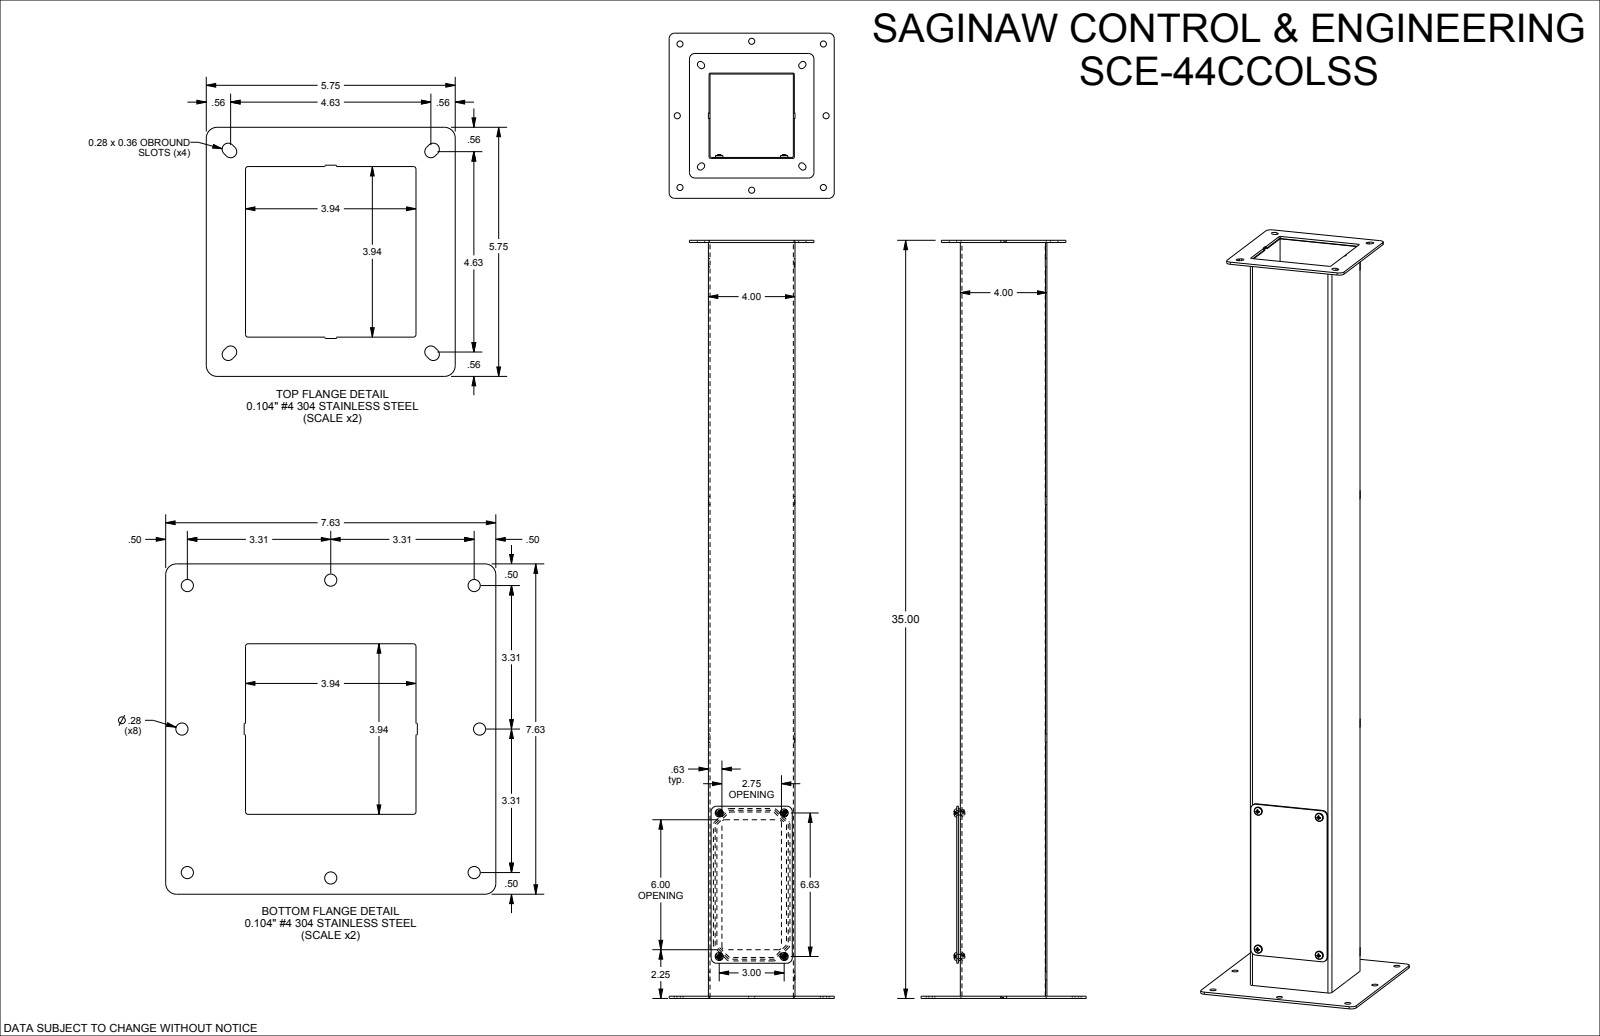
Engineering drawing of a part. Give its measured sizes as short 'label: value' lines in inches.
name: SCE-44CCOL
written by: SolidWorks 2019 (AUTOMOTIVE_DESIGN)
unit: in
bodies: 9 solids, 341 faces (141 planar, 92 cylindrical, 108 other)
size: 35 × 7.625 × 7.625
volume: 48.65 in³; area: 1 236 in²
holes: 8× ⌀0.281, 4× ⌀0.169, 4× ⌀0.218
bosses: 4× ⌀0.373, 4× ⌀0.188
rounds: 12× R0.25, 8× R0.045, 8× R0.08, 8× R0.125, 8× R0.141, 8× R0.205, 4× R0.15, 4× R0.225
face distances: 0.075, 3.925, 4, 3.85, 0.125, 34.875, 4.09, 4.015, 0.165, 0.09
hole spacings: 3.315, 7.519, 6.625, 4.861, 3, 6.875, 7.273, 9.369
